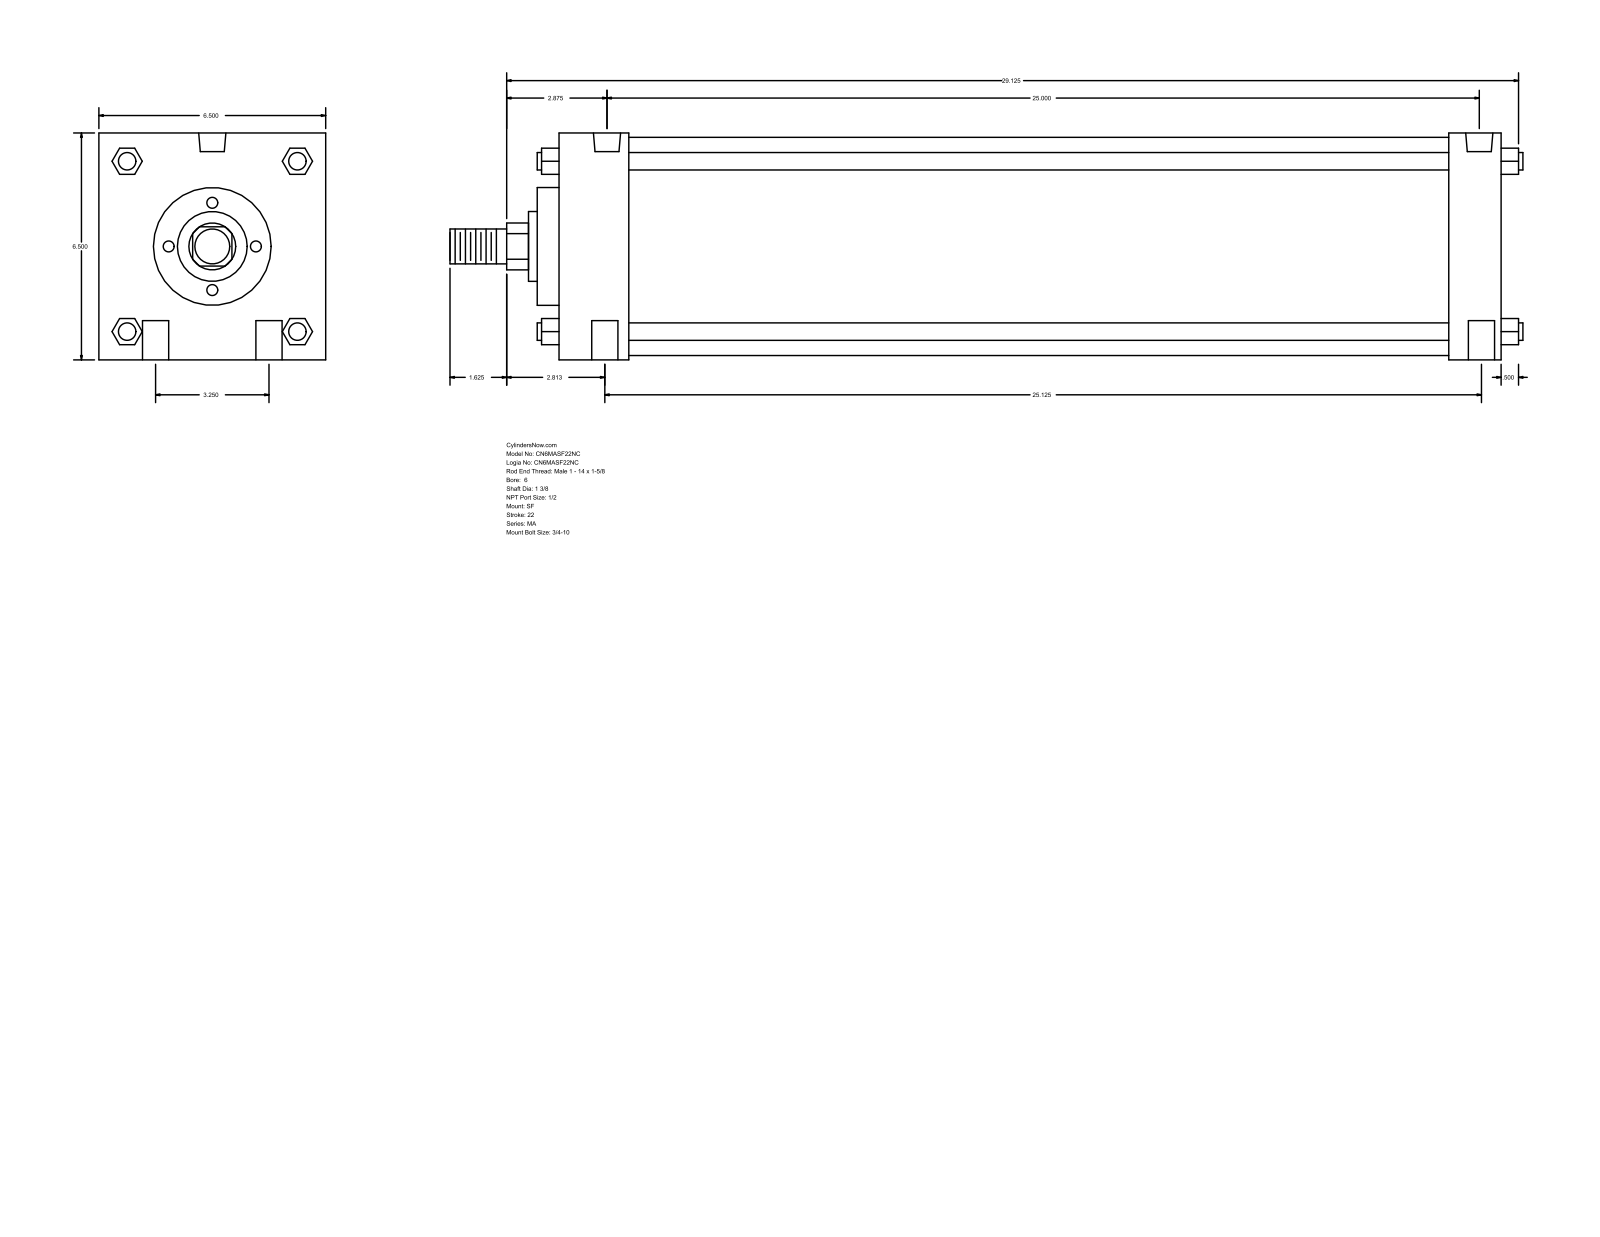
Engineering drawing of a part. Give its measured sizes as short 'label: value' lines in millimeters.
name: MA_SF__0600_1.375
written by: GSSL Pune (CONFIG_CONTROL_DESIGN)
unit: mm
bodies: 0 solids, 126 faces (95 planar, 31 cylindrical, 0 other)
size: 781.05 × 165.1 × 165.1
holes: 4× ⌀19.05, 2× ⌀17.46, 2× ⌀19.77
bosses: 4× ⌀12.7, 1× ⌀158.75, 1× ⌀85.72, 1× ⌀50.8, 1× ⌀34.92, 1× ⌀25.4
rounds: 1× R17.06
face distances: 165.1, 685.8, 647.7, 50.8, 38.1, 596.9, 635, 66.67, 15.87, 701.67
hole spacings: 41.3, 637.92, 82.54, 638.17, 643.49, 634.99, 635
